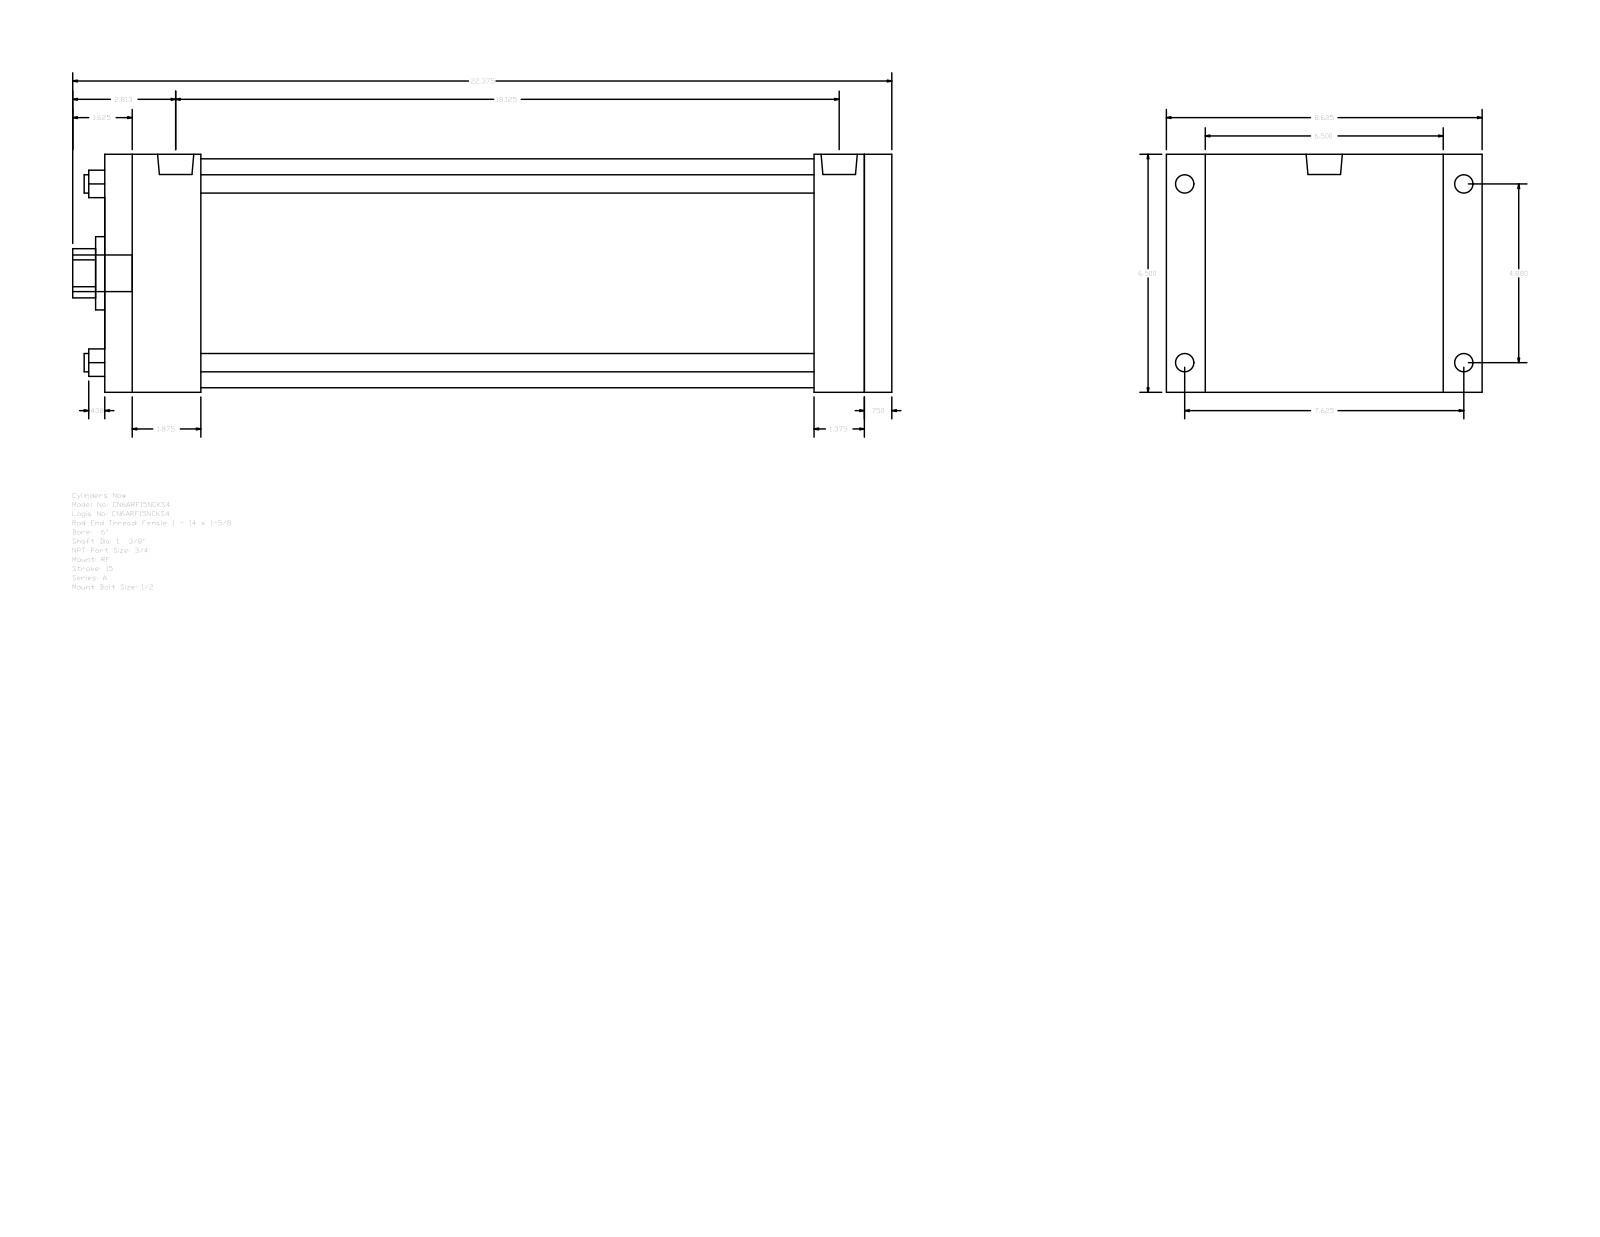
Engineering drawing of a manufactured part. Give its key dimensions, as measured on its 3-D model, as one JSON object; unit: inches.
{"part_name": "A_RF__0600_1.375", "step_written_by": "GSSL Pune (CONFIG_CONTROL_DESIGN)", "units": "inches", "bodies": {"solids": 0, "faces": 92, "planar": 64, "cylindrical": 28, "other": 0}, "overall_size": [22.375, 8.625, 6.5], "round_holes": [[0.5, 4], [1.375, 1], [2, 1], [6.25, 1]], "round_bosses_or_shafts": [[0.594, 4], [0.5, 4], [0.989, 2], [1, 1]], "partial_cylinders_radius": [[0.672, 1]], "face_to_face_distances": [6.5, 21.5, 20.75, 0.75, 2.625, 18.125, 18.875, 19.375, 16.75, 1.375], "hole_center_spacings": [3.451, 4.88, 6.902]}
